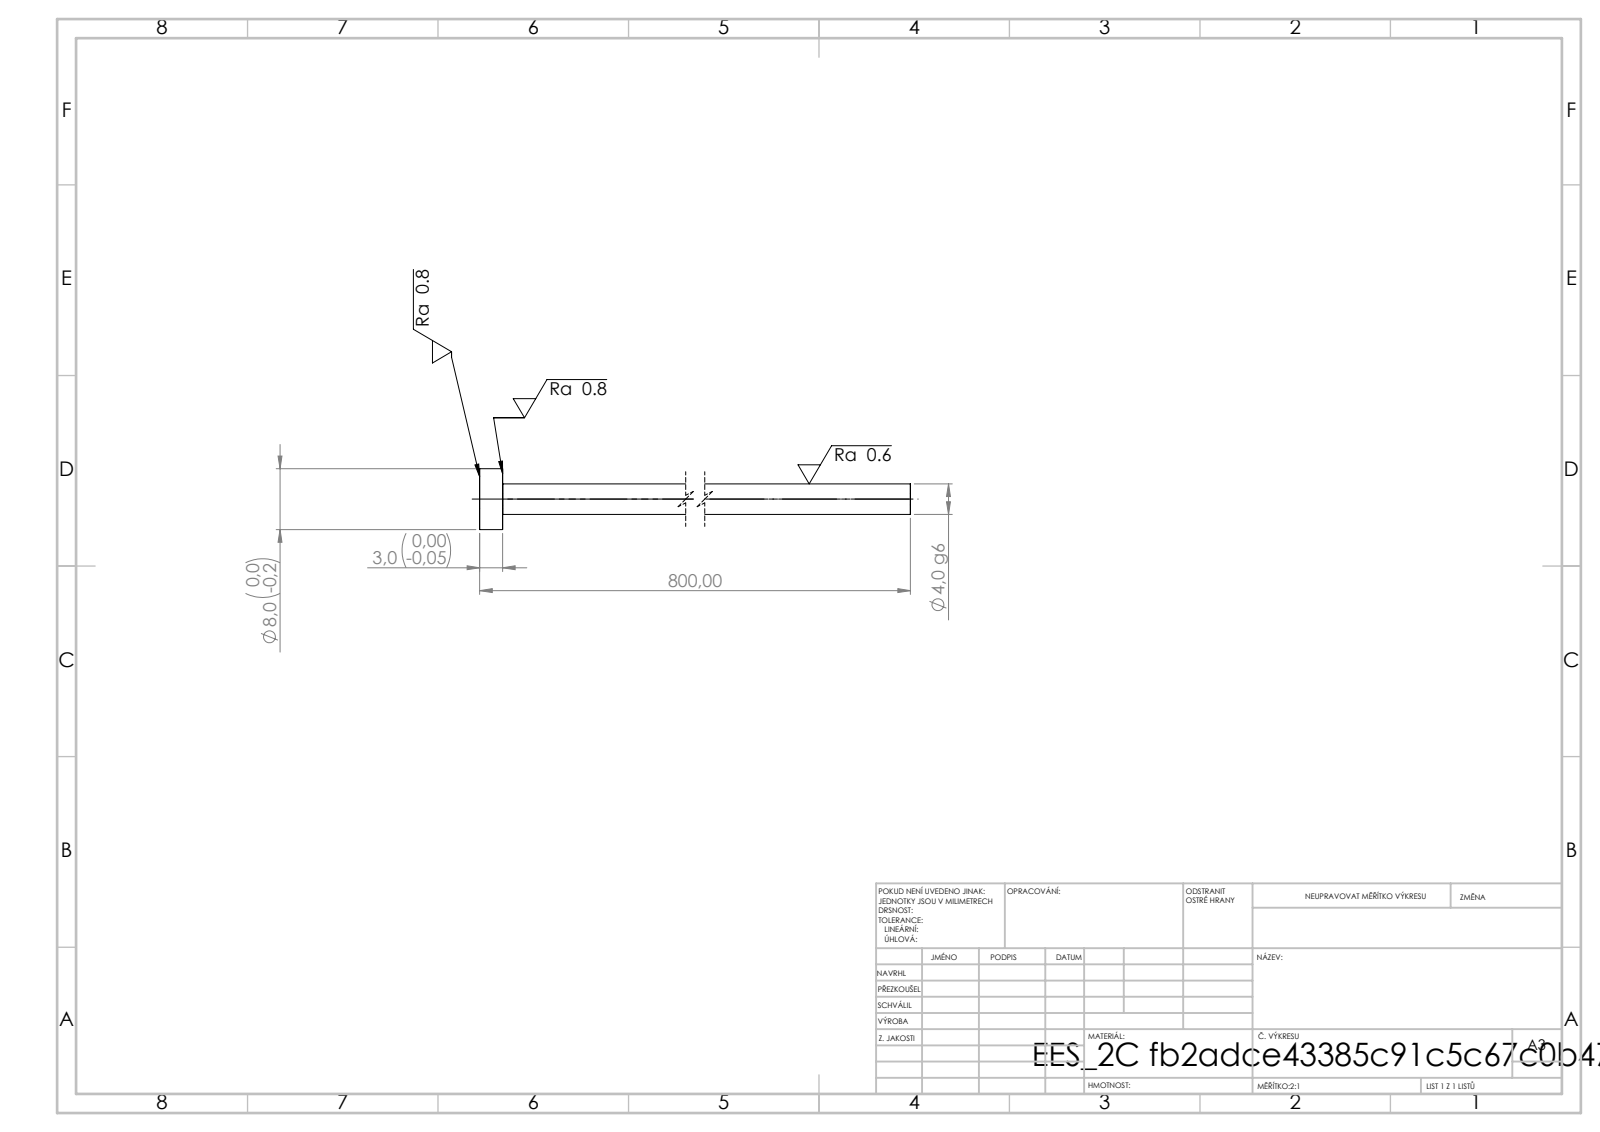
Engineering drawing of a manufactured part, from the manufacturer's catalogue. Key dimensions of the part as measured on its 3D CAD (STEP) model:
STEP written by: SolidWorks 2019 (CONFIG_CONTROL_DESIGN)
Units: millimetres
Bodies: 1 solid, 7 faces (3 planar, 4 cylindrical, 0 other)
Overall size (bounding box): 800 × 8 × 8
Volume: 10 166 mm³ · Surface area: 10 191 mm²
Round bosses / shafts (diameter × count): ⌀8 ×1, ⌀4 ×1
Main face-to-face distances: 3, 800, 797
